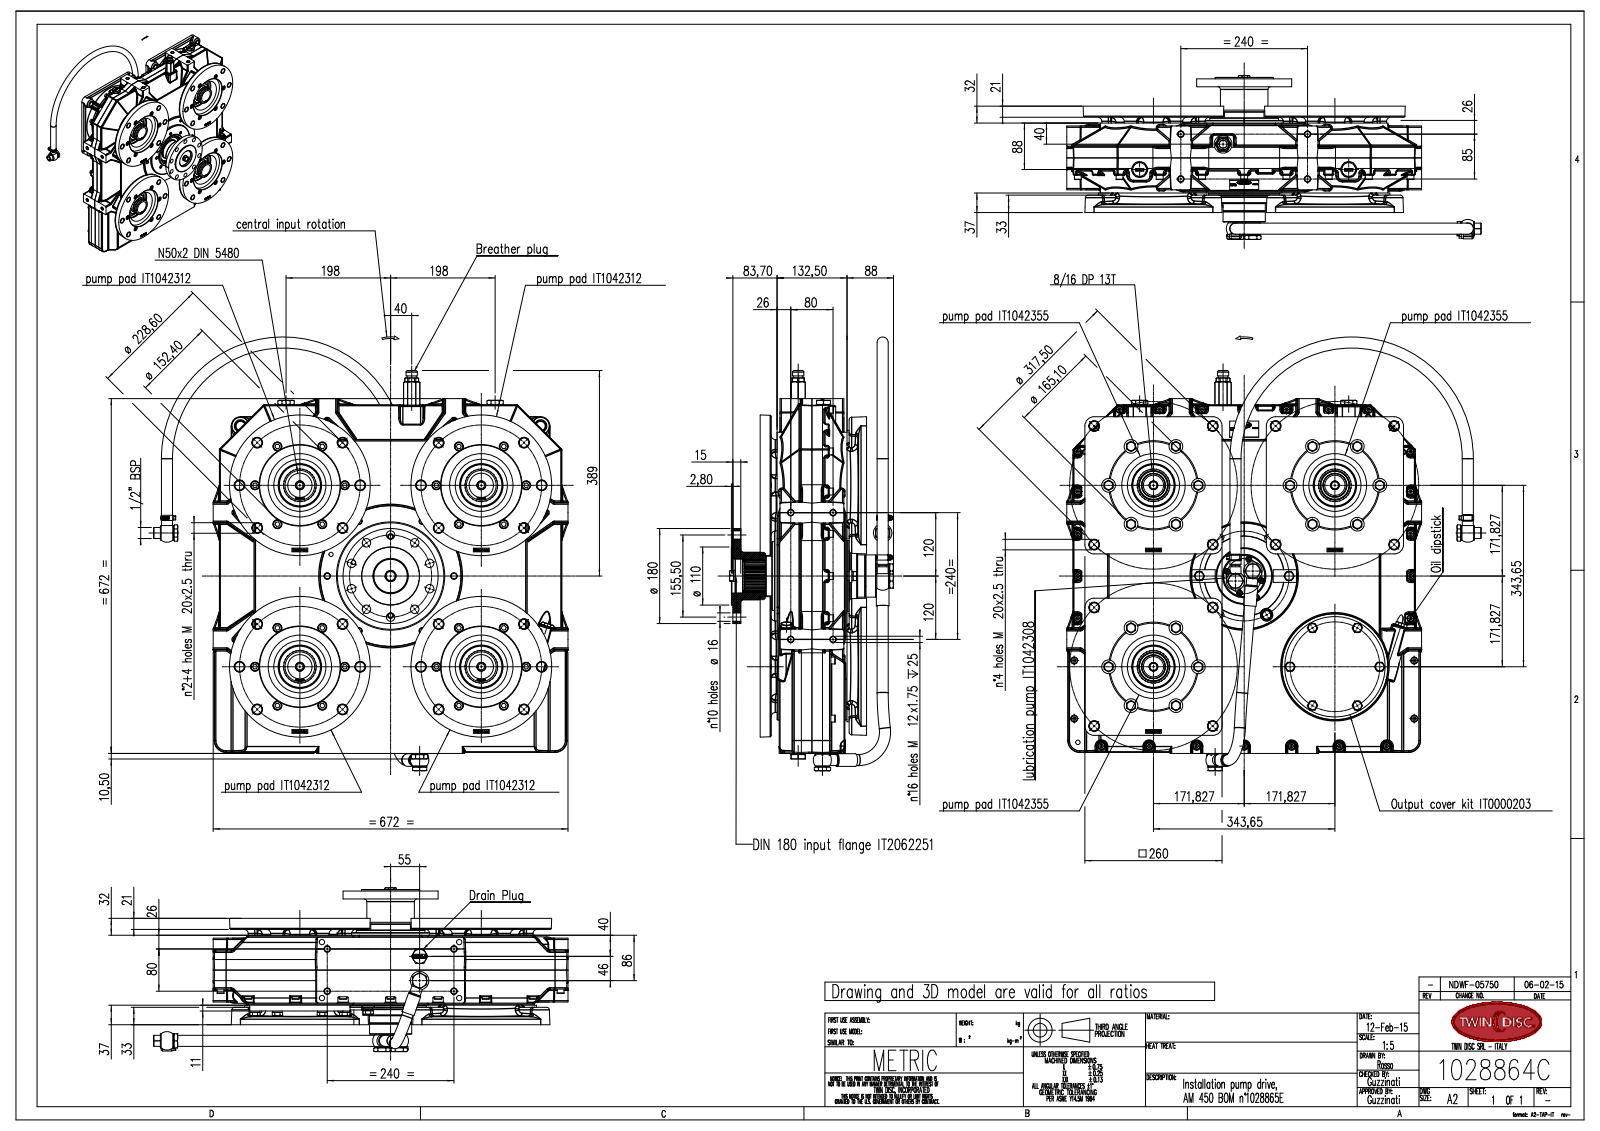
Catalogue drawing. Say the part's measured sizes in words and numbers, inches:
The part is named "IT1042355_rev00-installation; 1028864C; ITB00710000_rev01-installation; ITam450-006_rev00-installation (+8 more)". Its 3-D file was written by "SolidWorks 2007 (AUTOMOTIVE_DESIGN)". It is 80 solids with 13681 faces: 5379 planar, 3758 cylindrical and 4544 other. Overall it measures 32.423 by 30.907 by 12.224 inches. Its volume is 718.9 cubic inches and its surface area 8 376 square inches. Round holes: 68 of diameter 0.335, 40 of diameter 0.787, 36 of diameter 0.689, 33 of diameter 0.433, 28 of diameter 0.669, 26 of diameter 0.402, 18 of diameter 1.024, 17 of diameter 0.472, 17 of diameter 0.63, 12 of diameter 0.394, 10 of diameter 0.315, 10 of diameter 0.827. Round bosses or shafts: 33 of diameter 0.394, 28 of diameter 0.638, 28 of diameter 0.63, 28 of diameter 0.512, 28 of diameter 0.315, 9 of diameter 0.713, 6 of diameter 1.063, 6 of diameter 0.236. Partial cylindrical surfaces (rounded edges, fillets, slot ends): 324 of radius 0.098, 106 of radius 0.079, 68 of radius 0.197, 58 of radius 0.018, 48 of radius 0.315, 31 of radius 0.059, 8 of radius 0.039, 6 of radius 0.394. The main face-to-face distances are 0.157, 5.059, 3.031, 2.618, 2.461, 4.075, 6.476, 6.319, 3.858, 5.217. The hole center spacings are 4.724, 2.26, 2.953, 5.456, 7.765, 10.012, 11.841, 9.449.
